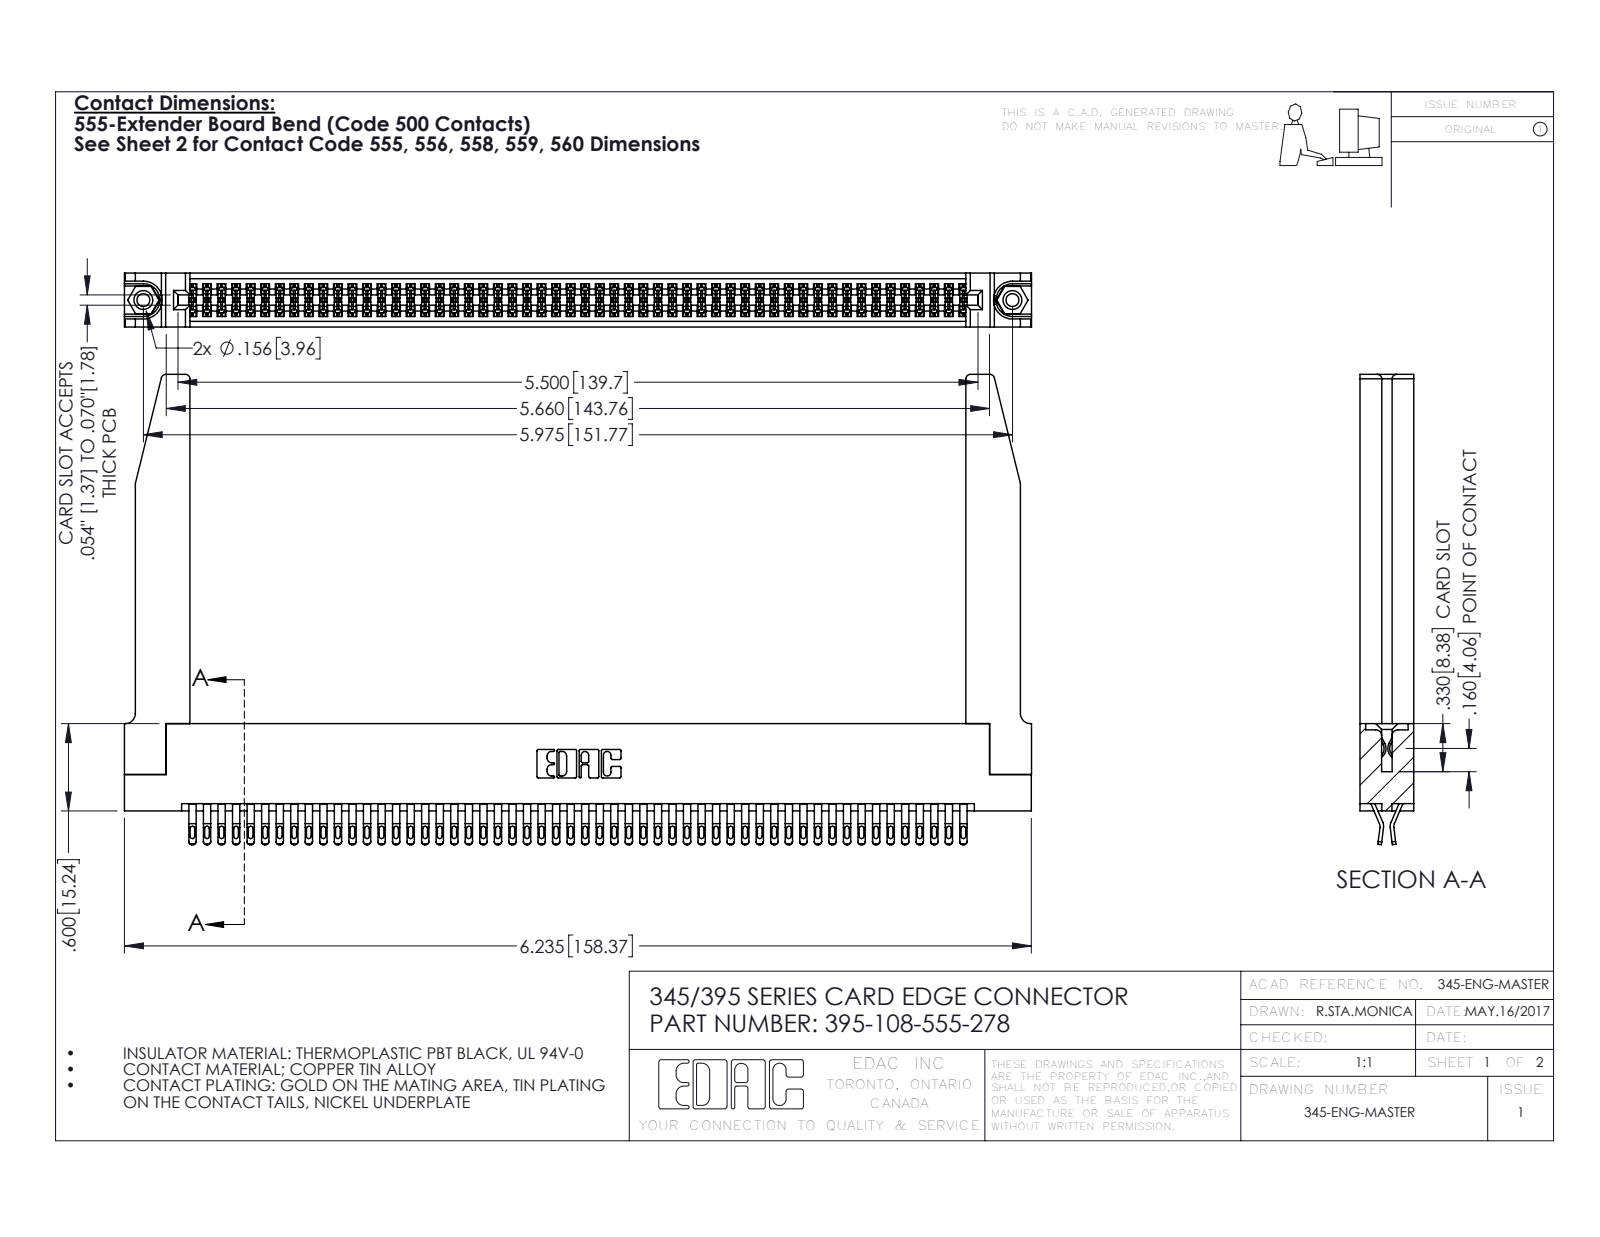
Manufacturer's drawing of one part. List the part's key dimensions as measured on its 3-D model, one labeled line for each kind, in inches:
Part name (STEP PRODUCT): 345 Part_Flush Mounting Lugs - 0.156 Dia-TH; 395-108-555-278; 345-220-078_345-220-078; 345-292-001_555 Tail (+1 more)
STEP written by: SolidWorks 2016 (CONFIG_CONTROL_DESIGN)
Units: inches
Bodies: 113 solids, 6408 faces (3570 planar, 2786 cylindrical, 52 other)
Overall size (bounding box): 6.236 × 3.232 × 0.37
Volume: 1.439 in³ · Surface area: 48.87 in²
Round holes (diameter × count): ⌀0.089 ×2, ⌀0.125 ×2, ⌀0.156 ×2, ⌀0.064 ×1
Round bosses / shafts (diameter × count): ⌀0.155 ×2
Partial cylindrical surfaces — rounded edges, fillets, slot ends (radius × count): R0.016 ×270, R0.02 ×216, R0.006 ×162, R0.01 ×22, R0.03 ×8, R0.007 ×6, R0.031 ×6, R0.026 ×3
Main face-to-face distances: 0.072, 0.37, 0.298, 0.025, 0.2, 0.098, 0.272, 0.225, 0.175, 0.148
Hole centre spacings: 0.27, 5.739, 5.975
